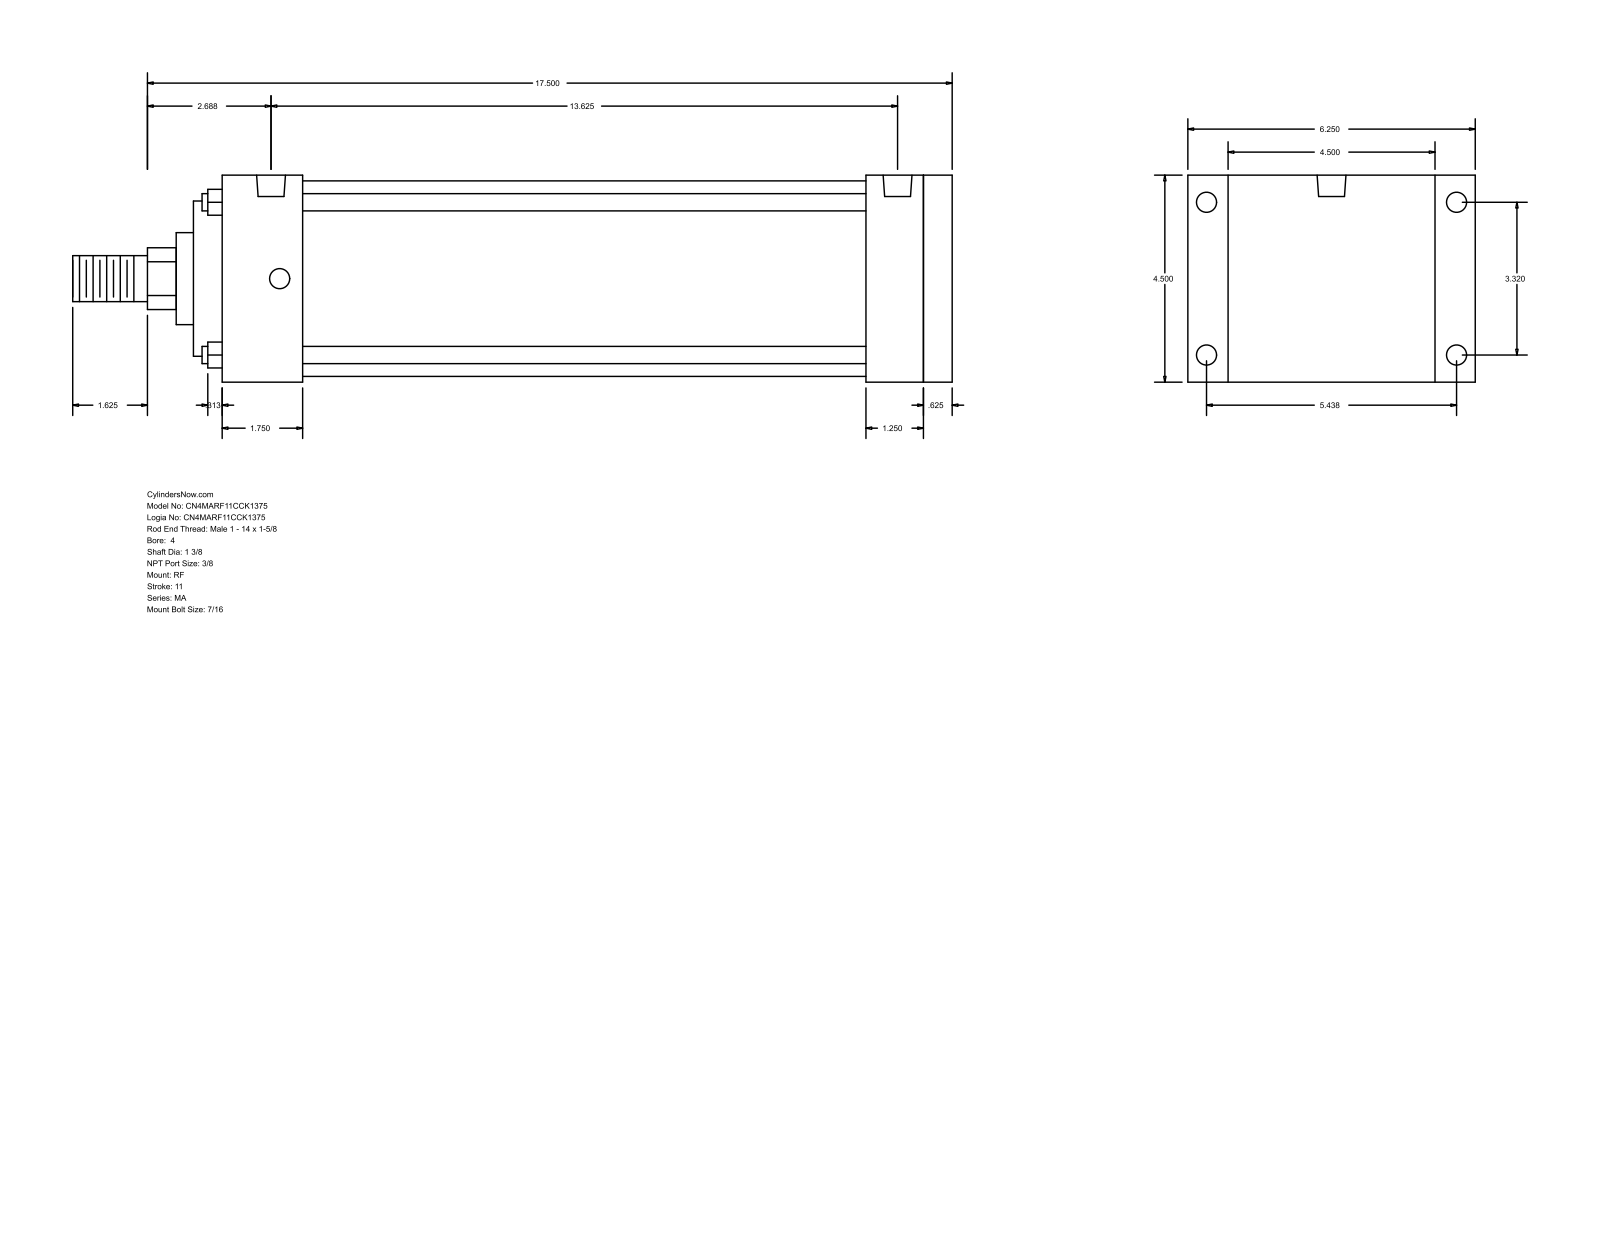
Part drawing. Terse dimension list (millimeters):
name: MA_RF__0400_1.375
written by: GSSL Pune (CONFIG_CONTROL_DESIGN)
unit: mm
bodies: 0 solids, 94 faces (65 planar, 29 cylindrical, 0 other)
size: 485.77 × 158.75 × 114.3
holes: 8× ⌀11.11, 2× ⌀15.93
bosses: 4× ⌀9.53, 1× ⌀107.95, 1× ⌀85.72, 1× ⌀50.8, 1× ⌀34.92, 1× ⌀25.4
rounds: 1× R17.06
face distances: 114.3, 403.23, 15.88, 387.35, 15.87, 403.22, 419.1, 22.23, 136.53, 371.48
hole spacings: 4.77, 84.32, 138.12, 161.82, 336.54, 341.31, 346.08
